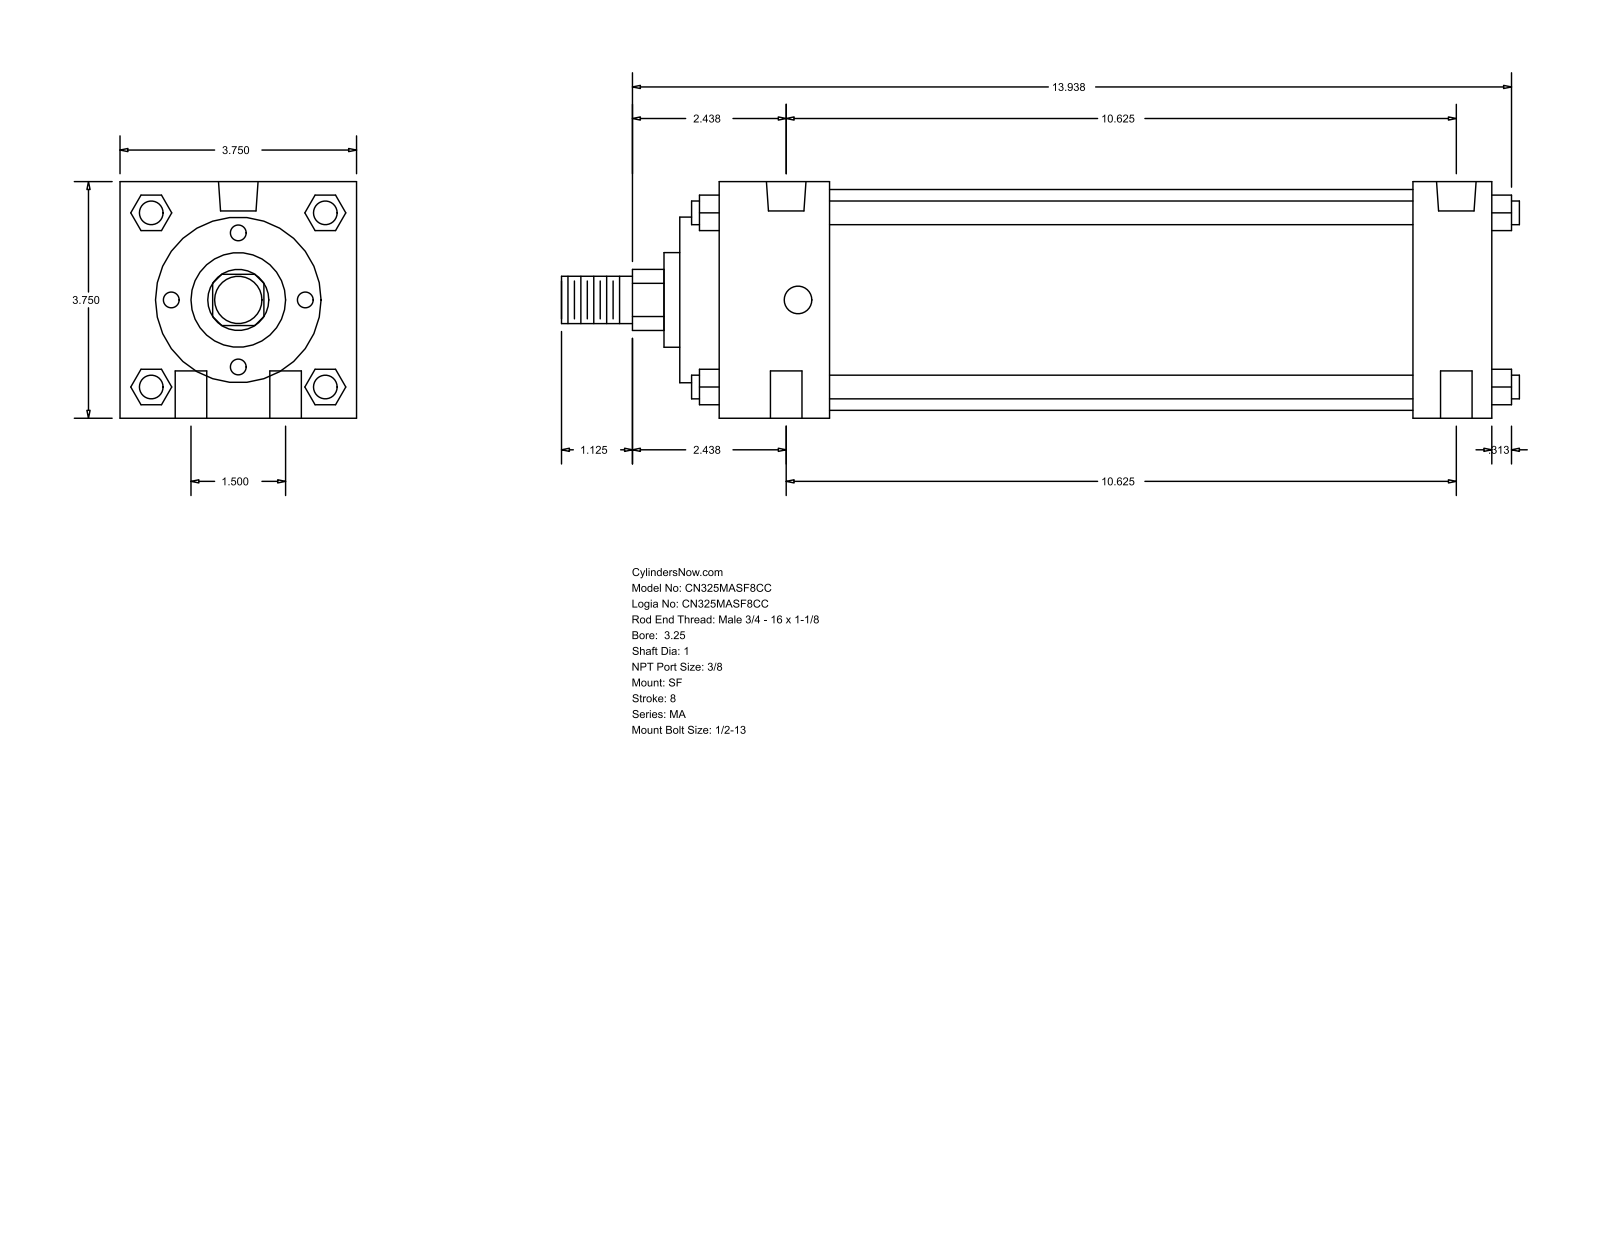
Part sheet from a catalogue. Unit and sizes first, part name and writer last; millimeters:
Units: millimetres
Overall size (bounding box): 385.76 × 95.25 × 95.25
Round holes (diameter × count): ⌀12.7 ×4, ⌀11.11 ×2, ⌀15.93 ×2
Round bosses / shafts (diameter × count): ⌀9.53 ×4, ⌀88.9 ×1, ⌀66.67 ×1, ⌀38.1 ×1, ⌀25.4 ×1, ⌀19.05 ×1
Partial cylindrical surfaces — rounded edges, fillets, slot ends (radius × count): R12.29 ×1
Main face-to-face distances: 95.24, 311.15, 327.02, 279.4, 31.75, 44.46, 234.94, 266.69, 15.87, 60.33
Hole centre spacings: 19.05, 270.55, 269.88, 38.1, 272.56, 260.35
Bodies: 0 solids, 126 faces (95 planar, 31 cylindrical, 0 other)
Part name (STEP PRODUCT): MA_SF__0325_1
STEP written by: GSSL Pune (CONFIG_CONTROL_DESIGN)
